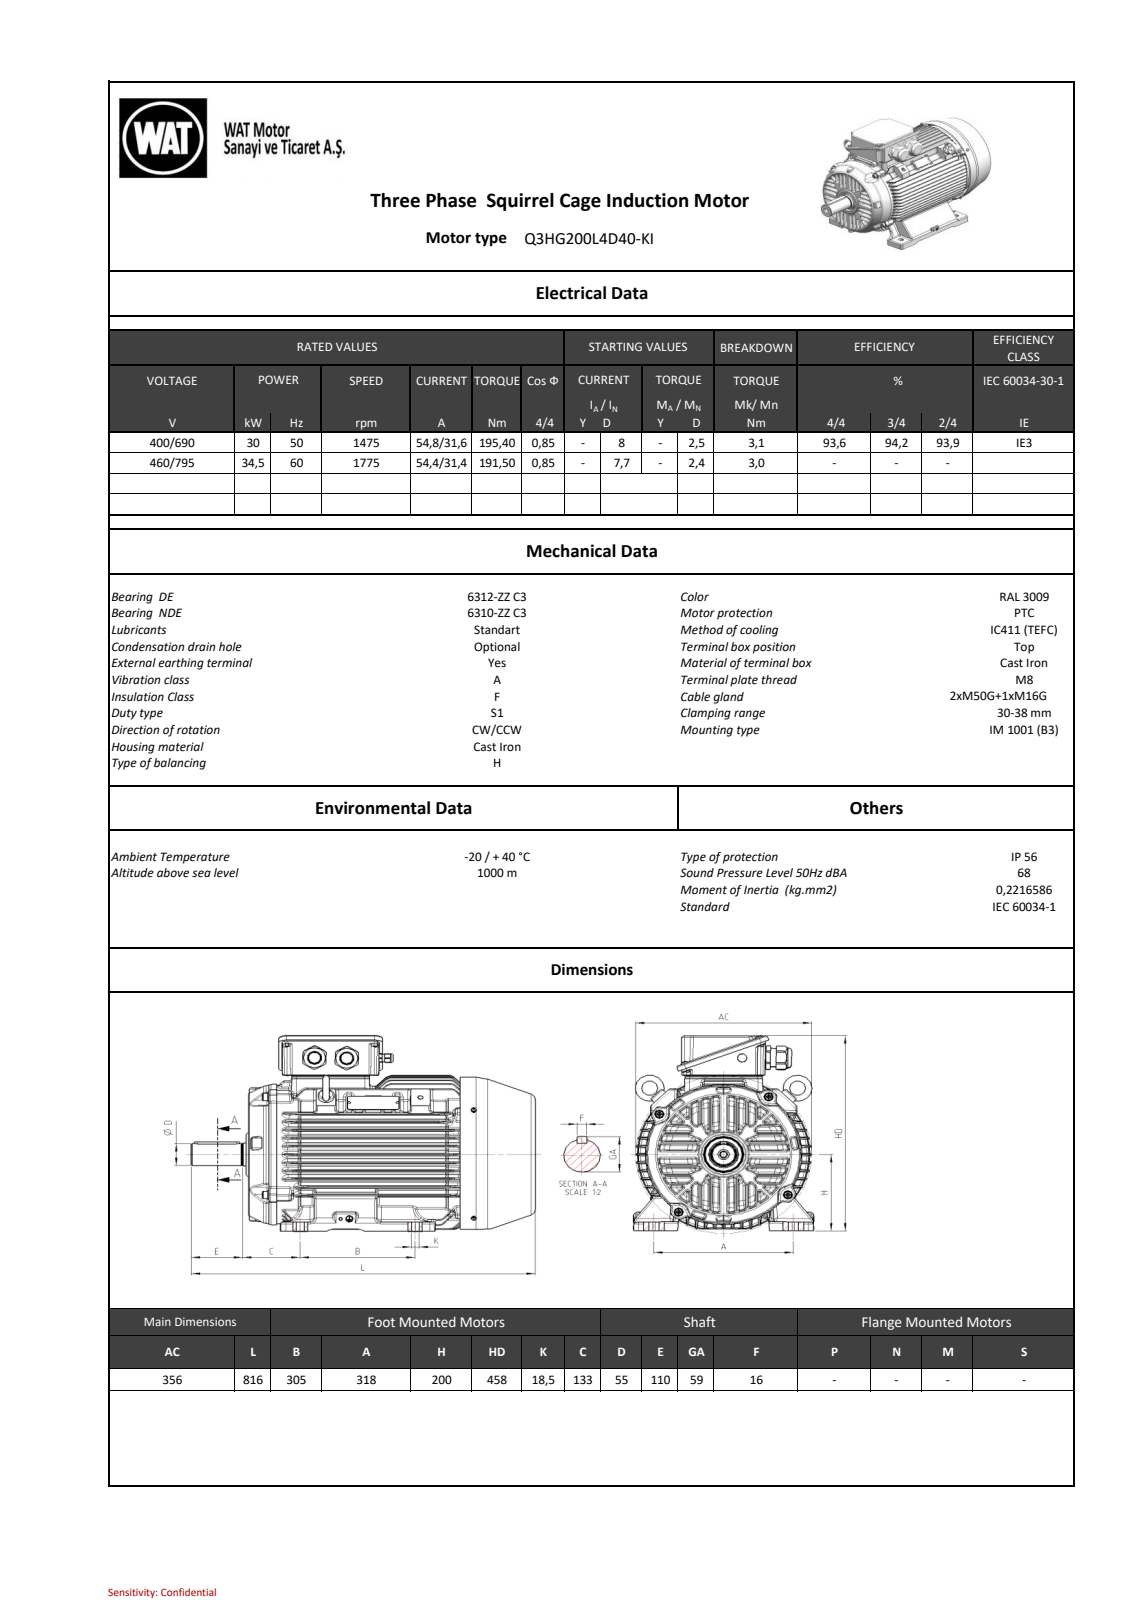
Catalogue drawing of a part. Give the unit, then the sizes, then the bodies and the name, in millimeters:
Units: millimetres
Overall size (bounding box): 815.5 × 457.73 × 391
Round holes (diameter × count): ⌀10.3 ×8, ⌀14 ×2, ⌀5 ×1, ⌀8 ×1, ⌀17.5 ×1, ⌀21 ×1, ⌀343.6 ×1
Round bosses / shafts (diameter × count): ⌀12 ×8, ⌀16 ×4, ⌀20 ×3, ⌀58 ×2, ⌀54.8 ×2, ⌀35 ×2, ⌀346 ×1, ⌀310 ×1
Partial cylindrical surfaces — rounded edges, fillets, slot ends (radius × count): R4 ×369, R3 ×171, R1.5 ×136, R2 ×104, R1.8 ×61, R5 ×49, R0.4 ×29, R10 ×13
Main face-to-face distances: 14.54, 14.46, 29, 29.14, 14.6, 43.6, 58.71, 43.79, 29.25, 14.65
Hole centre spacings: 158.01, 223.45, 54.87, 181.26, 258.86, 311.21, 316.01, 157.76
Bodies: 0 solids, 7068 faces (2115 planar, 1478 cylindrical, 3475 other)
Part name (STEP PRODUCT): C9017F38B806sx21
STEP written by: SIEMENS PLM Software NX 11.0 (AUTOMOTIVE_DESIGN)
